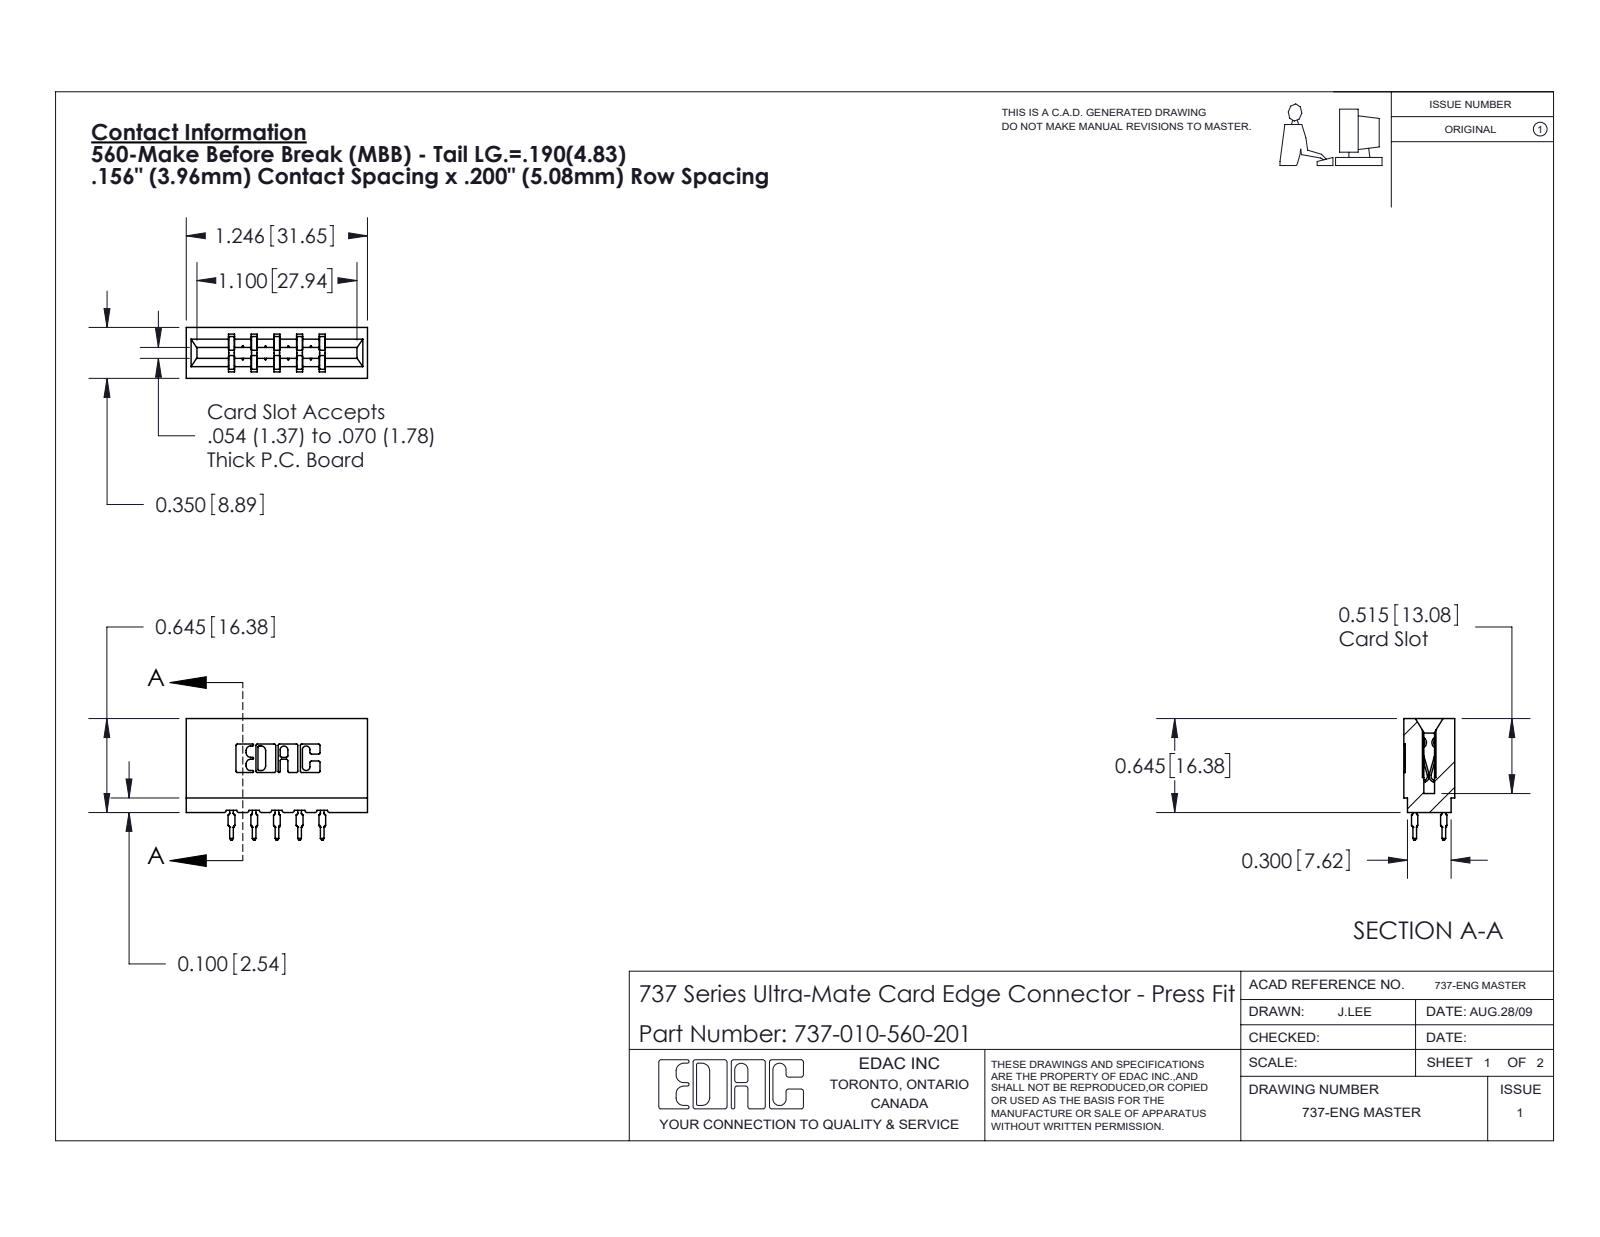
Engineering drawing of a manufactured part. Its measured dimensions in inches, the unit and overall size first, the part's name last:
Units: inches
Overall size (bounding box): 1.246 × 0.836 × 0.35
Partial cylindrical surfaces — rounded edges, fillets, slot ends (radius × count): R0.01 ×22, R0.021 ×20, R0.015 ×10, R0.005 ×8, R0.011 ×8, R0.007 ×6, R0.031 ×6, R0.026 ×3
Main face-to-face distances: 0.138, 0.212, 0.156, 0.35, 0.198, 0.312, 0.074, 0.354, 0.042, 0.025
Volume: 0.208 in³ · Surface area: 6.657 in²
Bodies: 11 solids, 1084 faces (569 planar, 255 cylindrical, 260 other)
Part name (STEP PRODUCT): 745-292-001_560; 737 Part_Insulator Option - 01; 737-010-560-201
STEP written by: SolidWorks 2020 (CONFIG_CONTROL_DESIGN)
